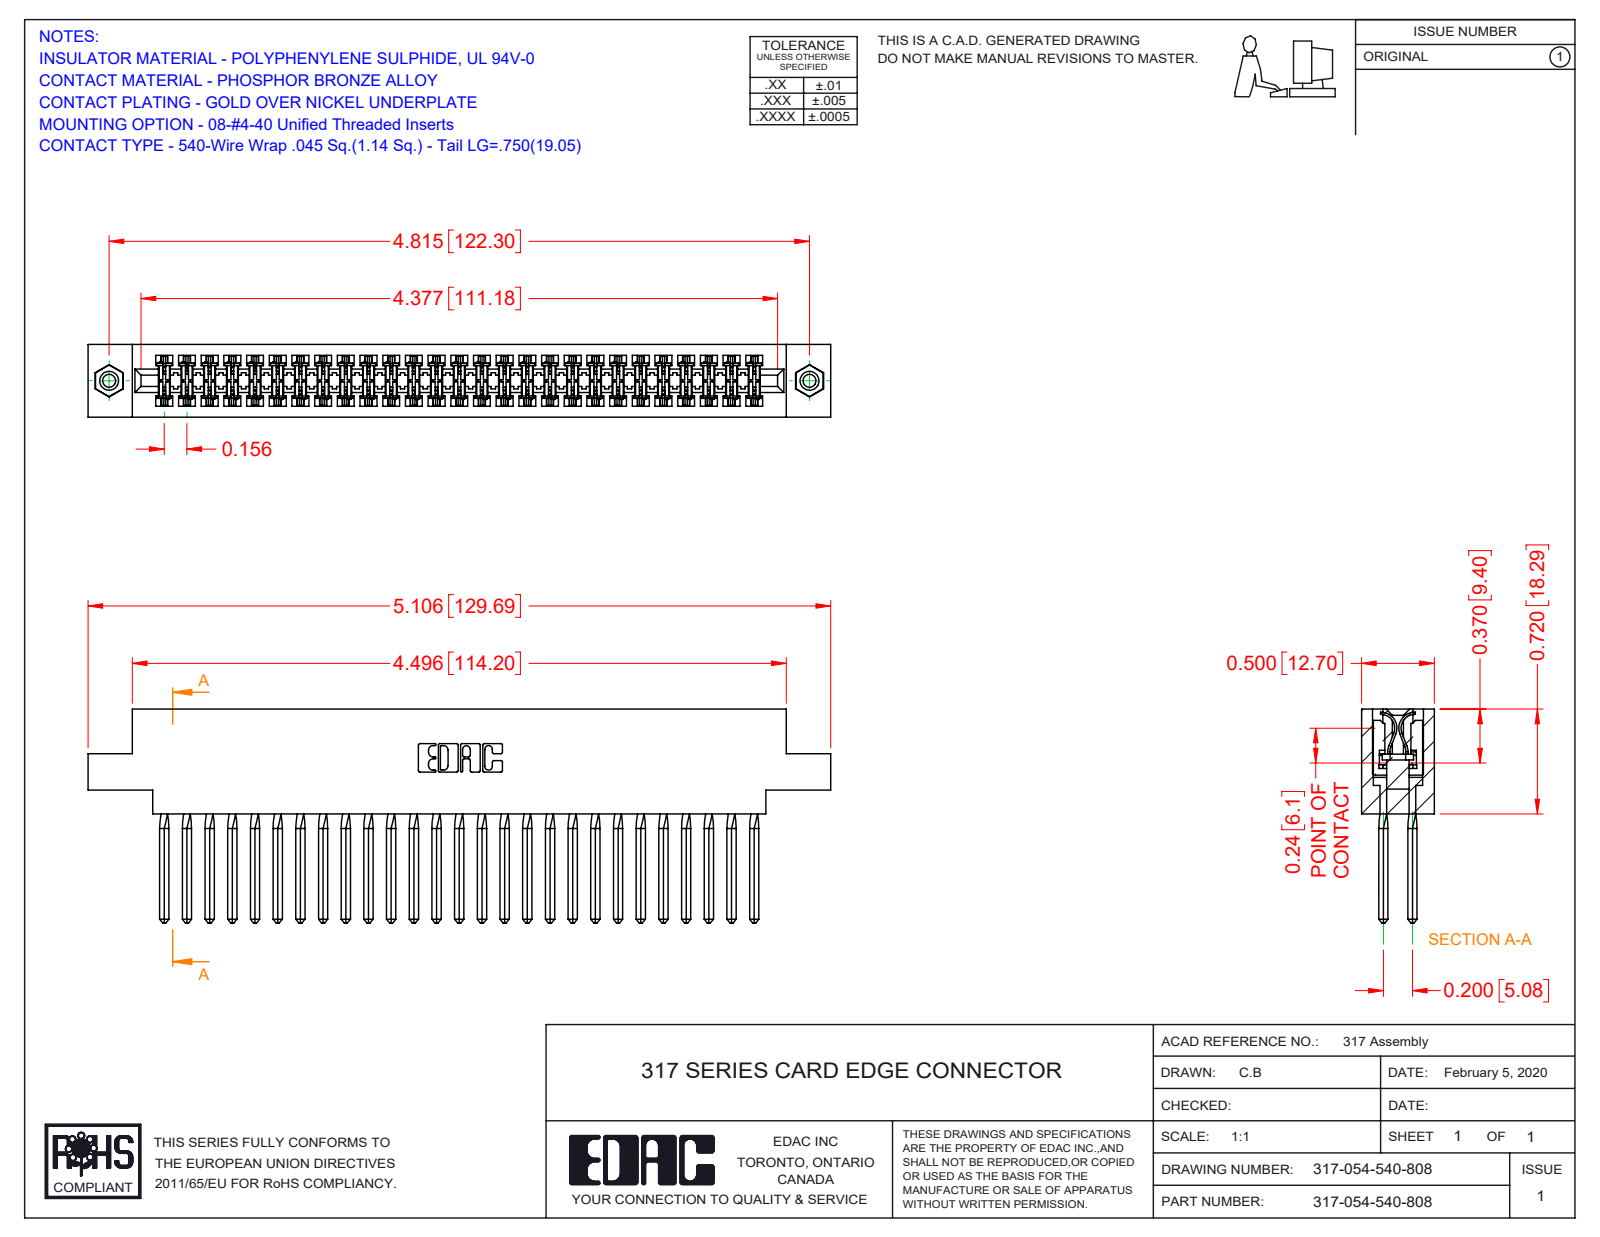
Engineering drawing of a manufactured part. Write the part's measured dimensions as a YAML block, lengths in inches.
part_name: "317-290-001_540; 345-250-001_345-250-003-102; 317-054-540-808; 317 Part_.156 Dia - TI"
step_written_by: "SolidWorks 2016 (CONFIG_CONTROL_DESIGN)"
units: inches
bodies: {solids: 57, faces: 4968, planar: 4032, cylindrical: 704, other: 232}
overall_size: [5.106, 1.47, 0.5]
volume: 1.297
surface_area: 48.27
round_holes:
  - {diameter: 0.089, count: 2}
  - {diameter: 0.125, count: 2}
  - {diameter: 0.156, count: 2}
round_bosses_or_shafts:
  - {diameter: 0.155, count: 2}
partial_cylinders:
  - {radius: 0.015, count: 108}
  - {radius: 0.01, count: 22}
  - {radius: 0.007, count: 6}
  - {radius: 0.031, count: 6}
  - {radius: 0.026, count: 3}
  - {radius: 0.095, count: 2}
  - {radius: 0.1, count: 2}
  - {radius: 0.11, count: 2}
face_to_face_distances: [0.5, 0.075, 0.425, 0.35, 0.11, 0.195, 0.094, 0.2, 0.72, 0.115]
hole_center_spacings: [4.815]
